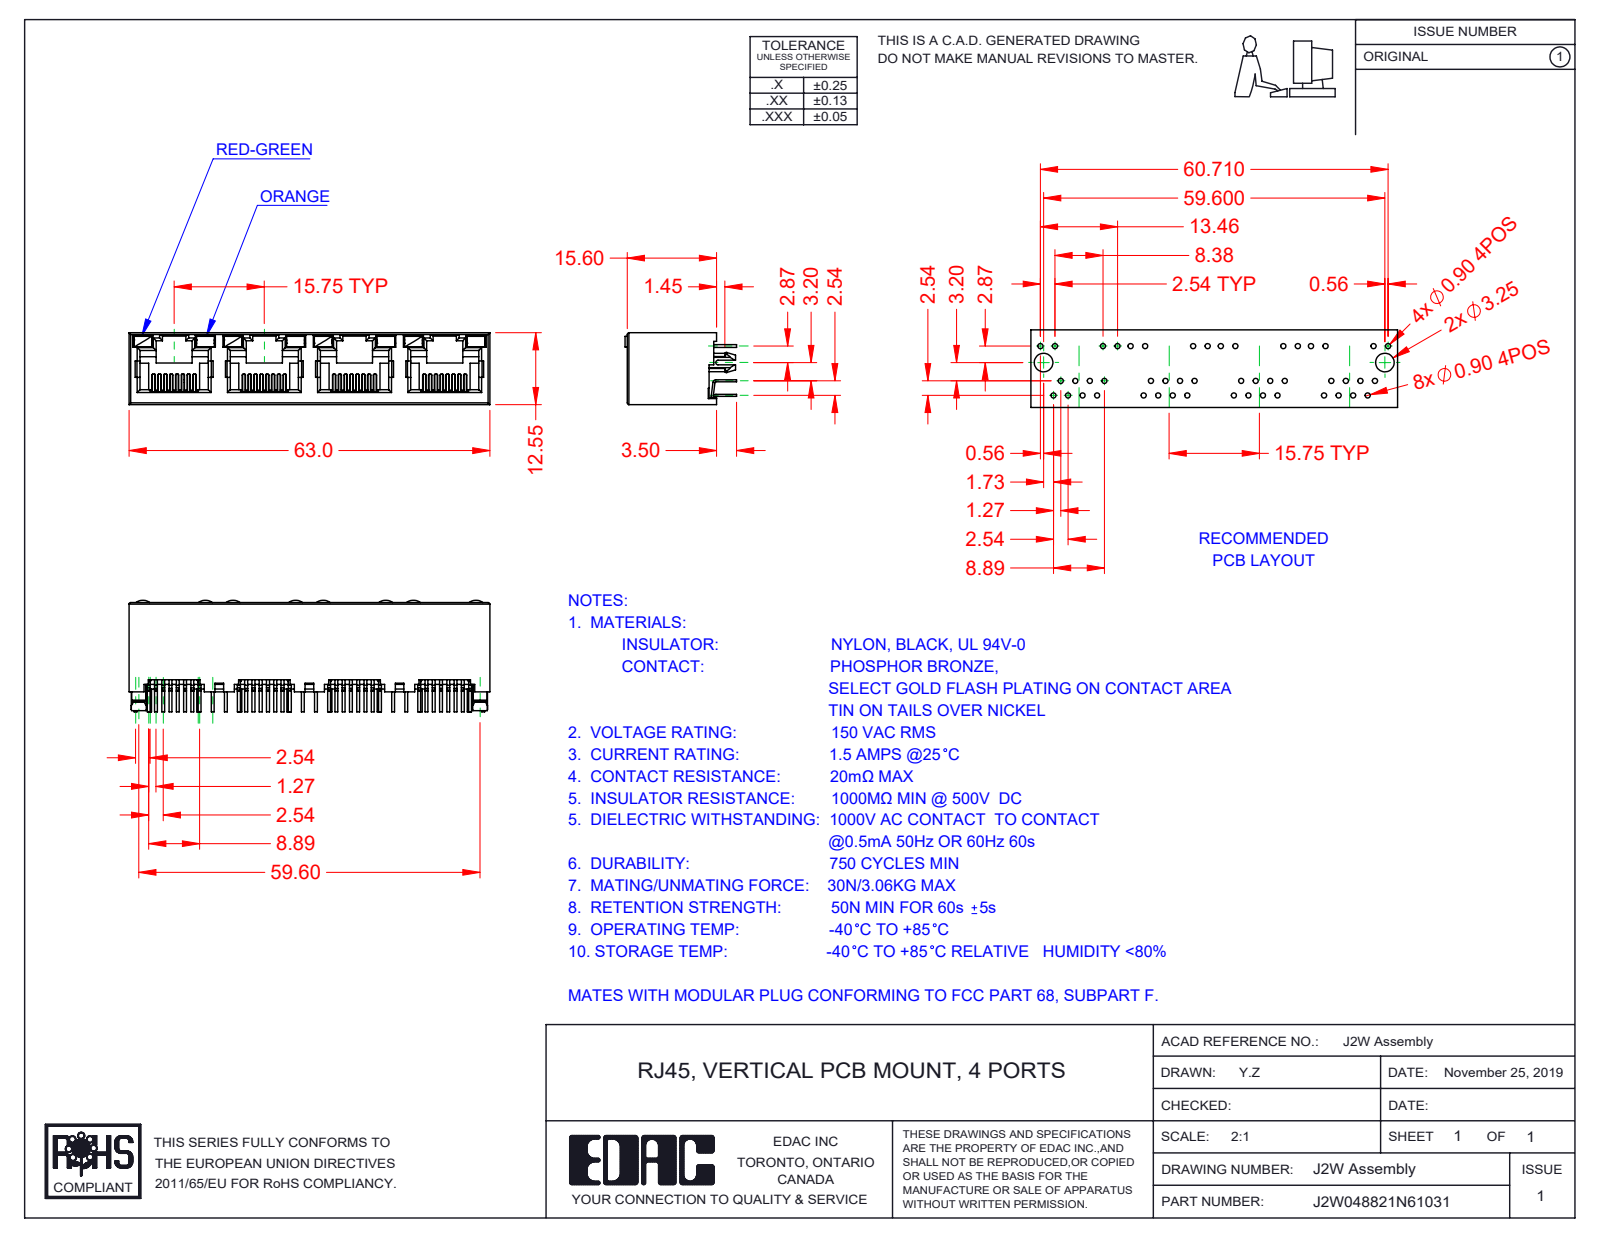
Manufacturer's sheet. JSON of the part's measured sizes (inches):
{"part_name": "J2W048821N64131; 2W Insulator; 2W LED LH_6-Red-Green; 2W Contacts (+2 more)", "step_written_by": "SolidWorks 2016 (CONFIG_CONTROL_DESIGN)", "units": "inches", "bodies": {"solids": 45, "faces": 3139, "planar": 2600, "cylindrical": 481, "other": 58}, "overall_size": [2.48, 0.768, 0.494], "volume_in3": 0.326, "surface_area_in2": 20.37, "partial_cylinders_radius": [[0.006, 64], [0.008, 29], [0.02, 28], [0.012, 14], [0.018, 8], [0.079, 8], [0.01, 2], [0.059, 2]], "face_to_face_distances": [0.494, 0.469, 0.026, 0.62, 0.014, 0.059, 0.031, 0.024, 0.445, 1.24]}
